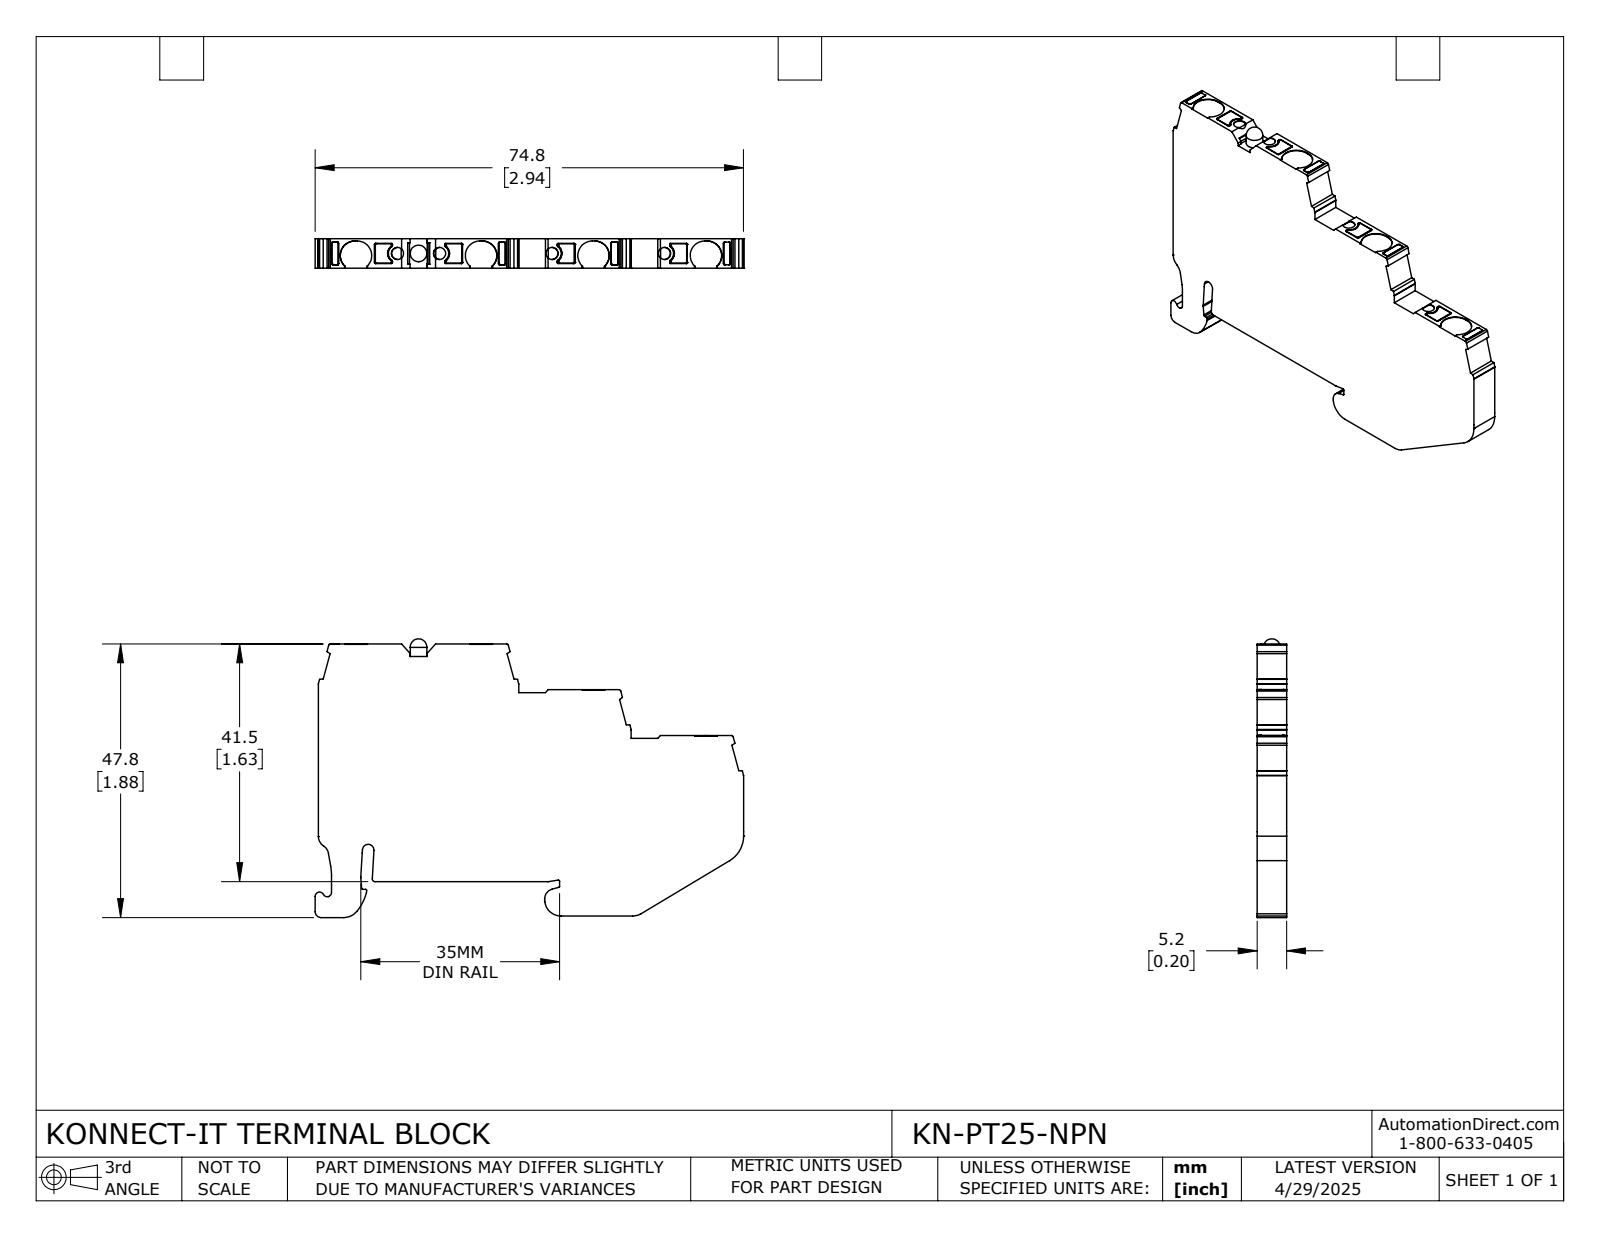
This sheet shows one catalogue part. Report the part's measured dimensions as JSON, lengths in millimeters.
{"part_name": "KN-PT25-NPN", "step_written_by": "SolidWorks 2024 (CONFIG_CONTROL_DESIGN)", "units": "millimeters", "bodies": {"solids": 1, "faces": 358, "planar": 201, "cylindrical": 146, "other": 11}, "overall_size": [74.8, 48.65, 5.15], "volume_mm3": 13781, "surface_area_mm2": 6772, "round_holes": [[2.1, 4]], "round_bosses_or_shafts": [[2.9, 1]], "partial_cylinders_radius": [[0.2, 68], [0.15, 16], [0.3, 8], [2.55, 8], [1.5, 4], [1.55, 4], [1, 3], [2, 3]], "face_to_face_distances": [5.15, 8, 6, 16, 7.99, 15.99, 74.25, 7.9, 8.1, 0.4], "hole_center_spacings": [7.34, 19.63, 19.64, 26.98, 39.27, 46.61]}
